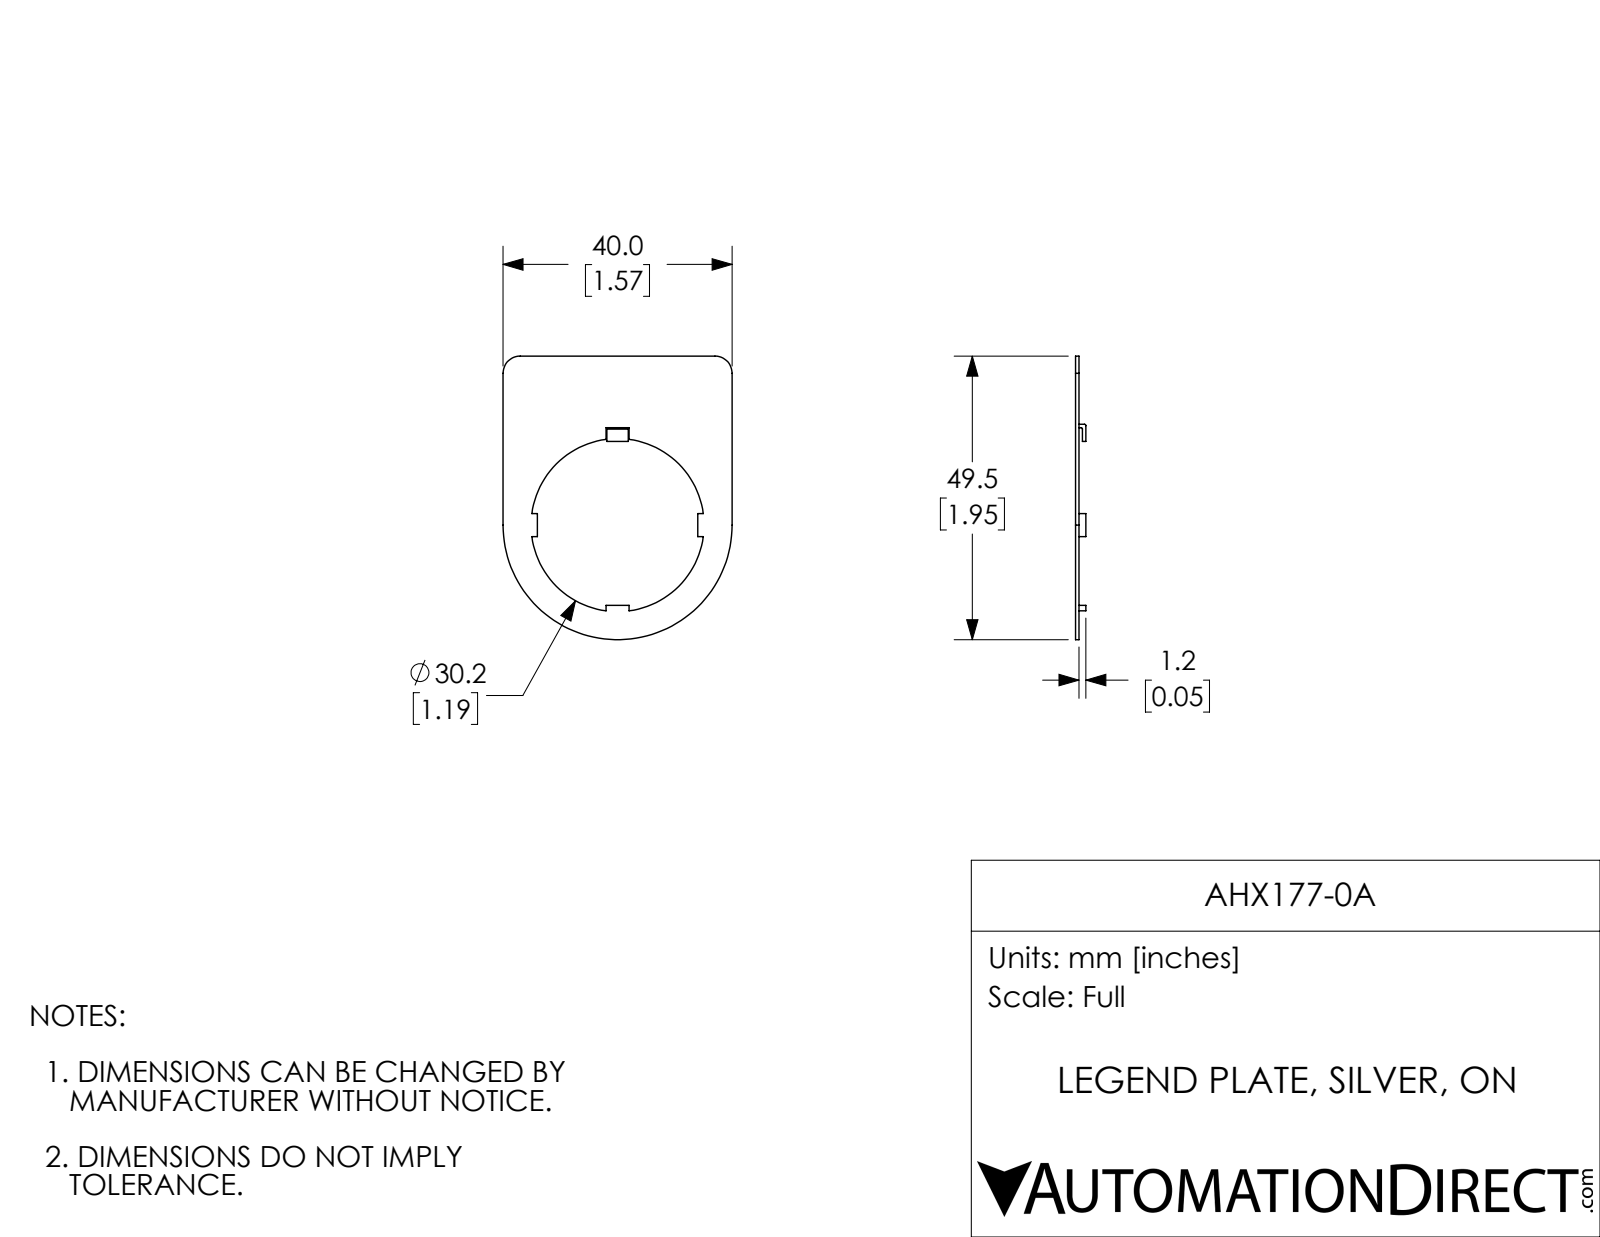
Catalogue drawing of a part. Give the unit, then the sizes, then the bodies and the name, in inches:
Units: inches
Overall size (bounding box): 1.949 × 1.575 × 0.071
Round holes (diameter × count): ⌀1.189 ×1
Partial cylindrical surfaces — rounded edges, fillets, slot ends (radius × count): R0.01 ×2, R0.118 ×2, R0.787 ×1
Main face-to-face distances: 0.024, 0.047, 0.071, 1.575, 0.038, 0.236, 1.339, 0.198, 1.377, 1.141
Volume: 0.041 in³ · Surface area: 3.736 in²
Bodies: 1 solid, 38 faces (29 planar, 9 cylindrical, 0 other)
Part name (STEP PRODUCT): AHX177-0A
STEP written by: SolidWorks 2017 (AUTOMOTIVE_DESIGN)
